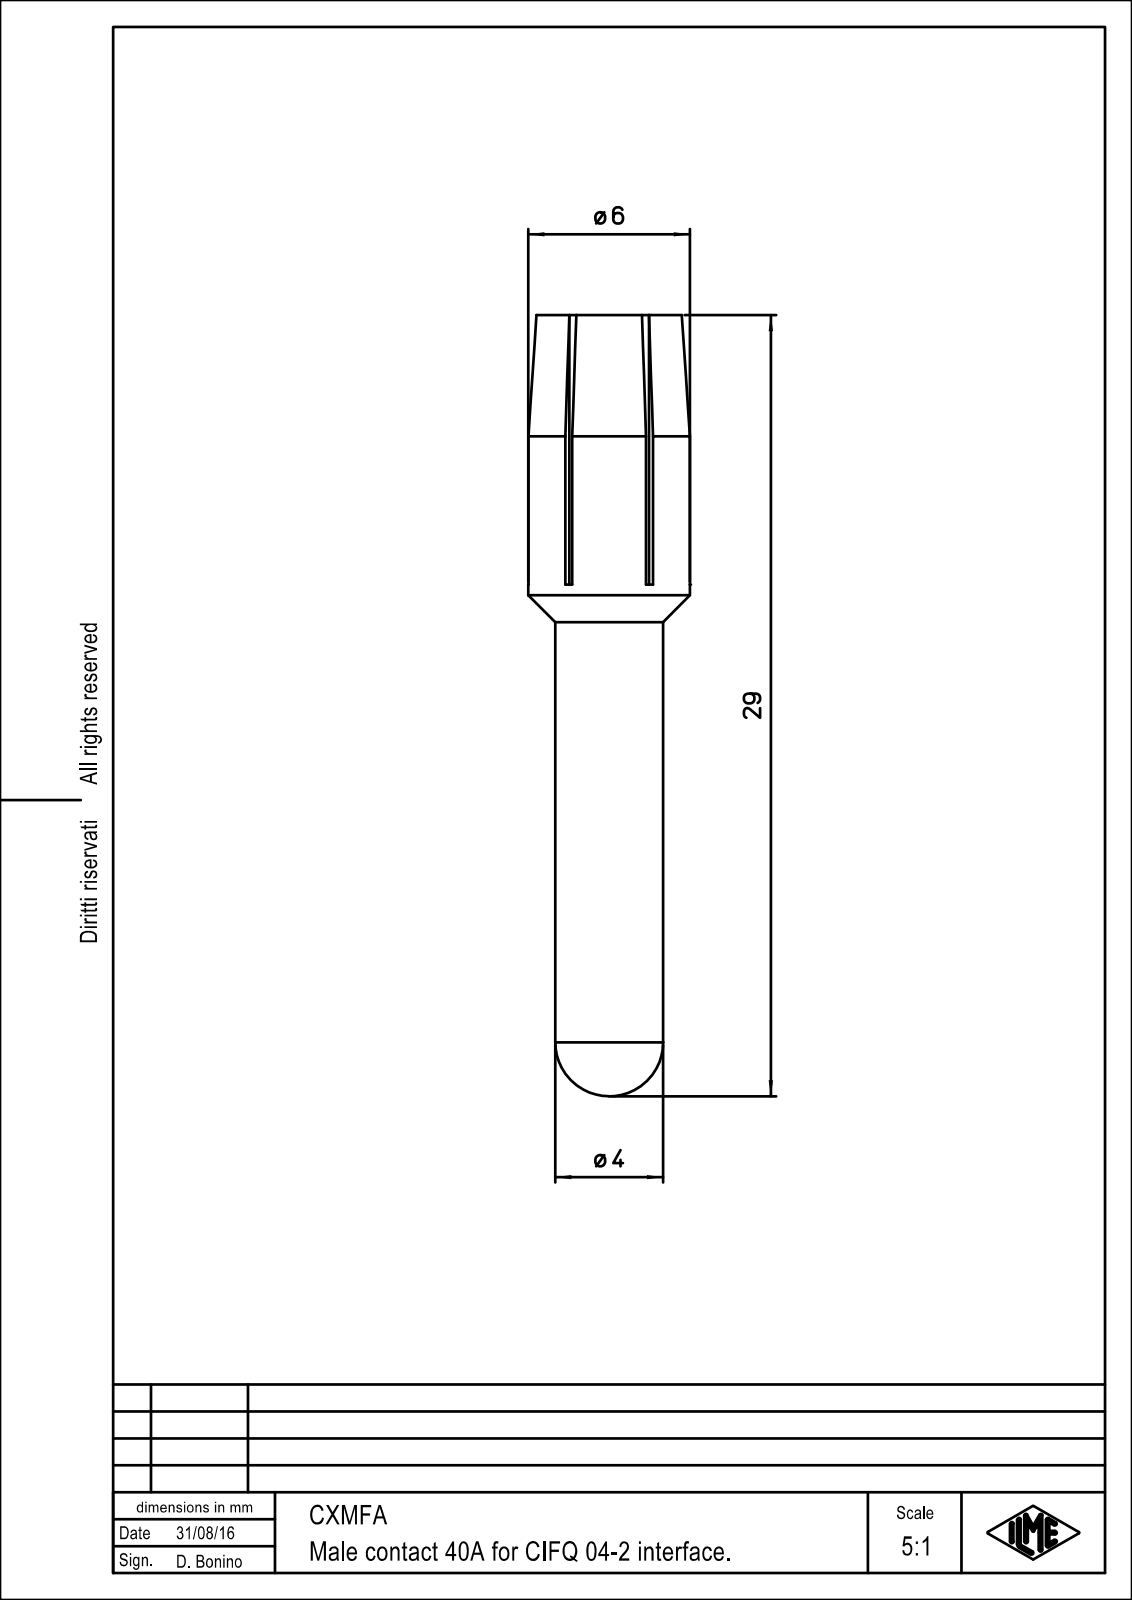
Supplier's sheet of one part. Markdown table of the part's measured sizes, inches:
| quantity | value |
| --- | --- |
| part name | CXMFA |
| STEP written by | PTC Creo Elements/Direct Modeling 19.0B 21-Mar-2015 (C) Parametric Technology GmbH (AUTOMOTIVE_DESIGN) |
| units | inches |
| bodies | 1 solid, 57 faces (31 planar, 10 cylindrical, 16 other) |
| overall size | 1.142 × 0.236 × 0.236 |
| volume | 0.023 in³ |
| surface area | 1.04 in² |
| round holes (diameter × count) | 0.165 × 1 |
| round bosses / shafts (diameter × count) | 0.236 × 1, 0.157 × 1 |
| main face-to-face distances | 0.019, 0.018, 0.394, 0.012 |
